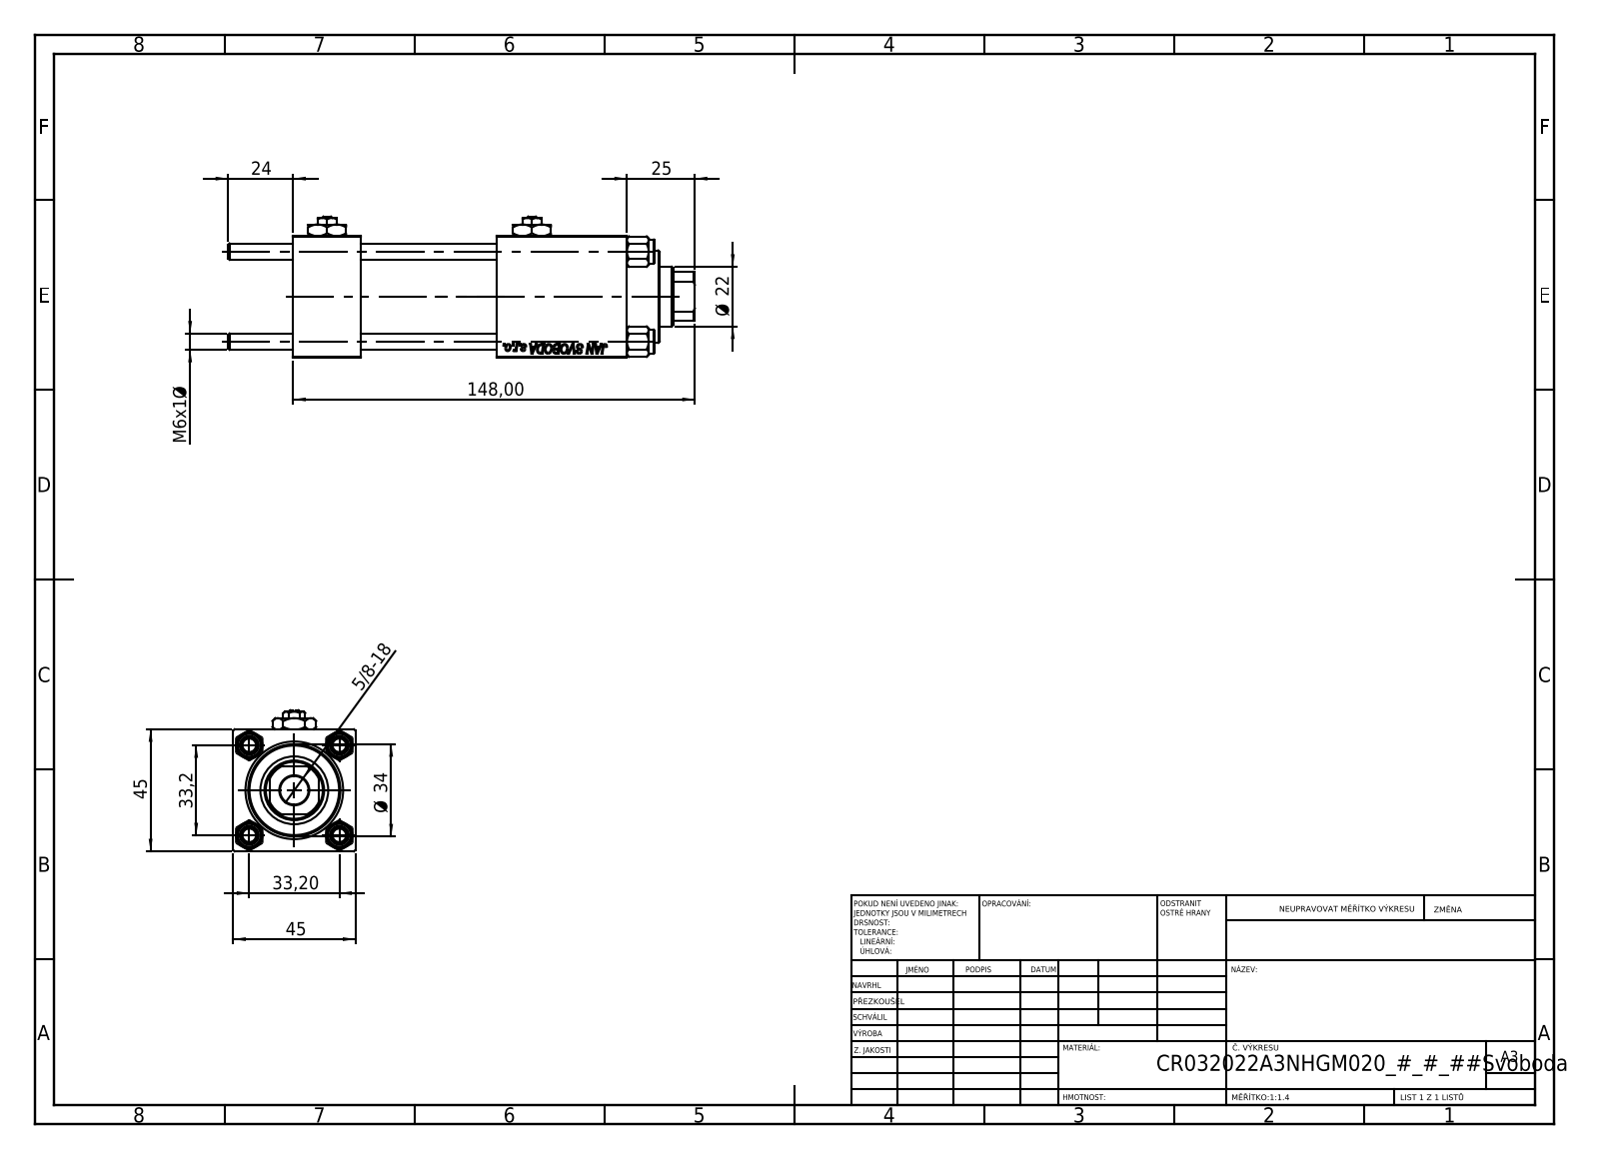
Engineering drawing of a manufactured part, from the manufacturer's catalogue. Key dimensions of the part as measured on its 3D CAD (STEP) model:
Part name (STEP PRODUCT): CR025_012_A_0_G_A_G_M_020_+#_##_TYCINKA; Zatka_pro_OIL_PORT; NUT_M5; V215CR_VCP (+2 more)
STEP written by: SolidWorks 2019 (CONFIG_CONTROL_DESIGN)
Units: millimetres
Bodies: 13 solids, 1232 faces (566 planar, 88 cylindrical, 578 other)
Overall size (bounding box): 172 × 52 × 45
Volume: 212 720 mm³ · Surface area: 78 882 mm²
Round holes (diameter × count): ⌀6 ×4, ⌀7 ×2, ⌀13.16 ×2, ⌀20 ×2, ⌀10.5 ×1, ⌀22 ×1, ⌀24 ×1, ⌀25 ×1, ⌀32 ×1, ⌀33 ×1
Round bosses / shafts (diameter × count): ⌀9 ×4, ⌀38 ×1, ⌀34 ×1
Partial cylindrical surfaces — rounded edges, fillets, slot ends (radius × count): R10.5 ×1
Main face-to-face distances: 45, 25, 123, 50, 75, 98, 48, 44.8, 94.3, 69.3
Hole centre spacings: 23.48, 33.2, 46.95, 75.5
